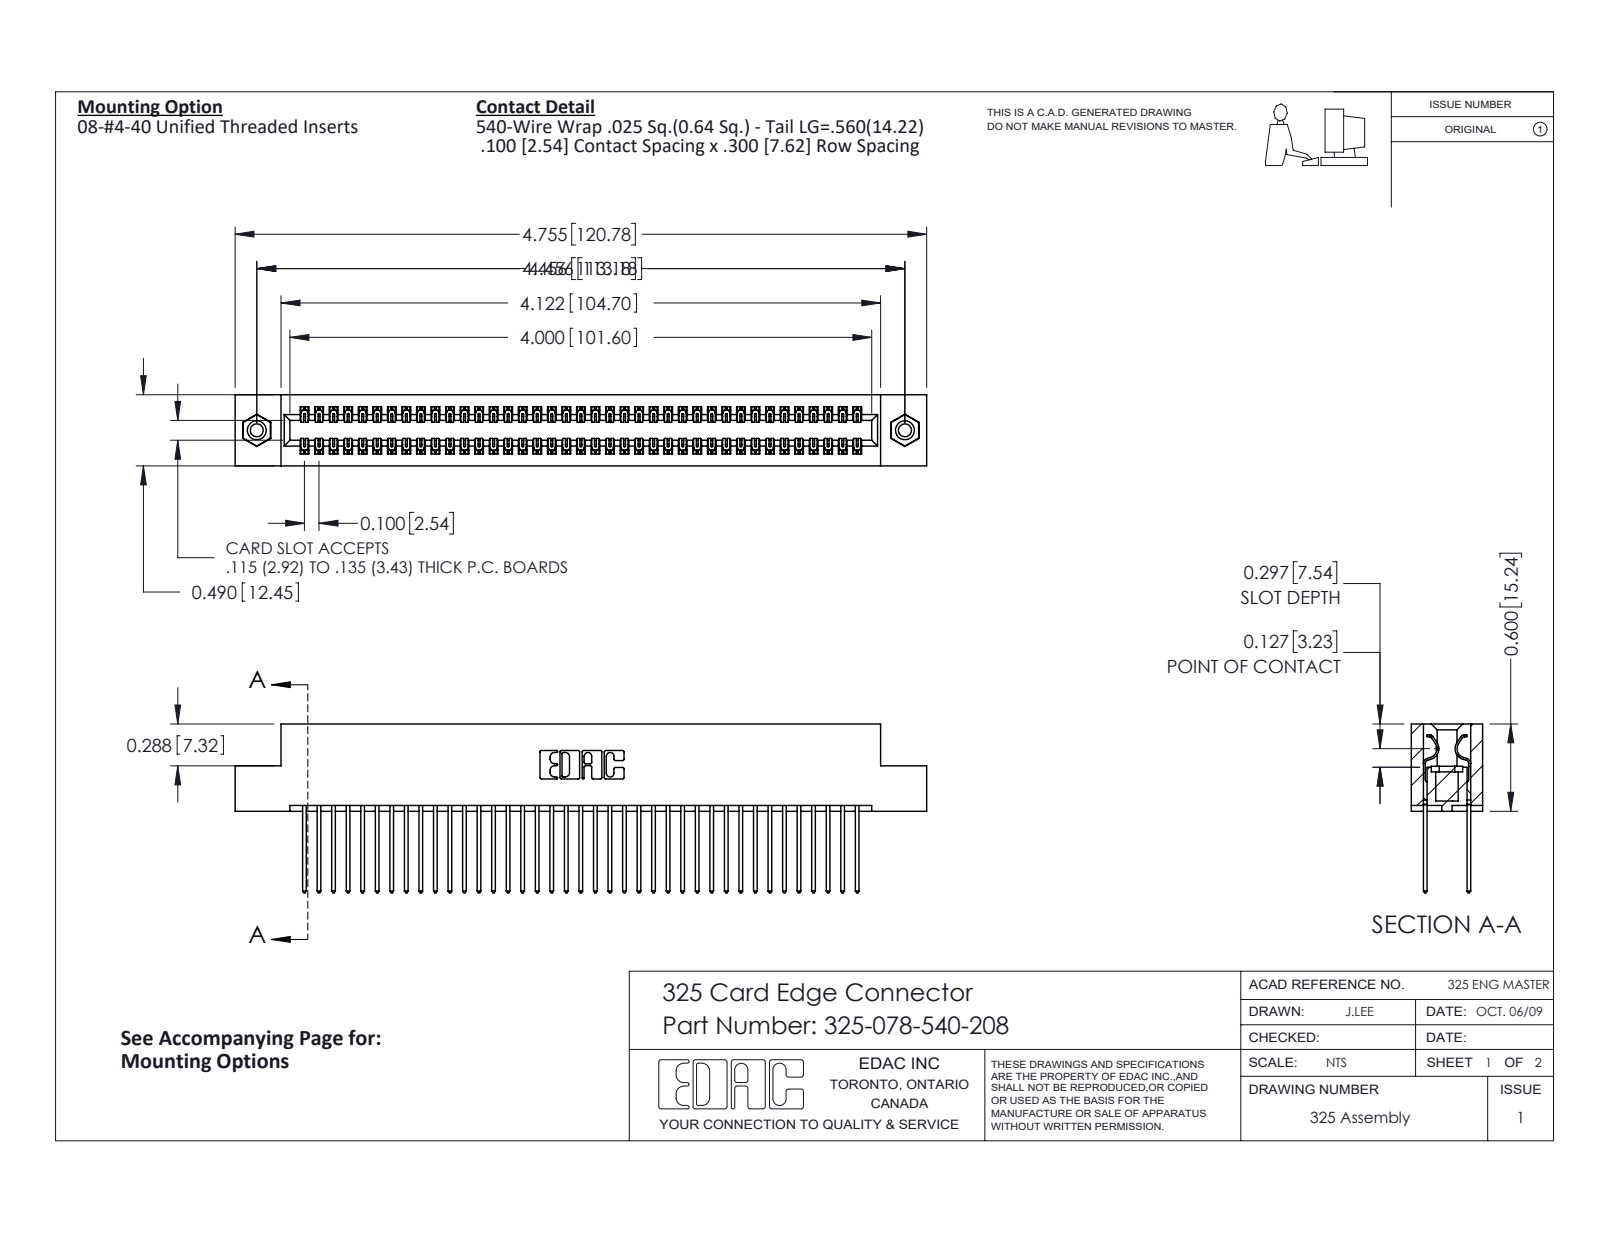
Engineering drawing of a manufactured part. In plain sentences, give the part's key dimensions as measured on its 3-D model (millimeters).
The part is named "325-078-540-208; 345-250-001_345-250-003-102; 325-292-001_325-293-140; 325 Part_TI". Its 3-D file was written by "SolidWorks 2016 (CONFIG_CONTROL_DESIGN)". It is 81 solids with 4230 faces: 2910 planar, 1304 cylindrical and 16 other. Overall it measures 120.8 by 29.5 by 12.4 millimeters. Its volume is 15 800 cubic millimeters and its surface area 20 540 square millimeters. Round holes: 2 of diameter 2.3, 2 of diameter 3.2, 2 of diameter 4.1. Round bosses or shafts: 2 of diameter 3.9. Partial cylindrical surfaces (rounded edges, fillets, slot ends): 117 of radius 0.2, 78 of radius 0.3, 22 of radius 0.3, 6 of radius 0.2, 6 of radius 0.8, 3 of radius 0.7, 2 of radius 0.4, 2 of radius 0.6. The main face-to-face distances are 2.1, 10.3, 7.6, 2.7, 9.7, 0.6, 12.4, 8.3, 7, 14.2. The hole center spacings are 113.2.
